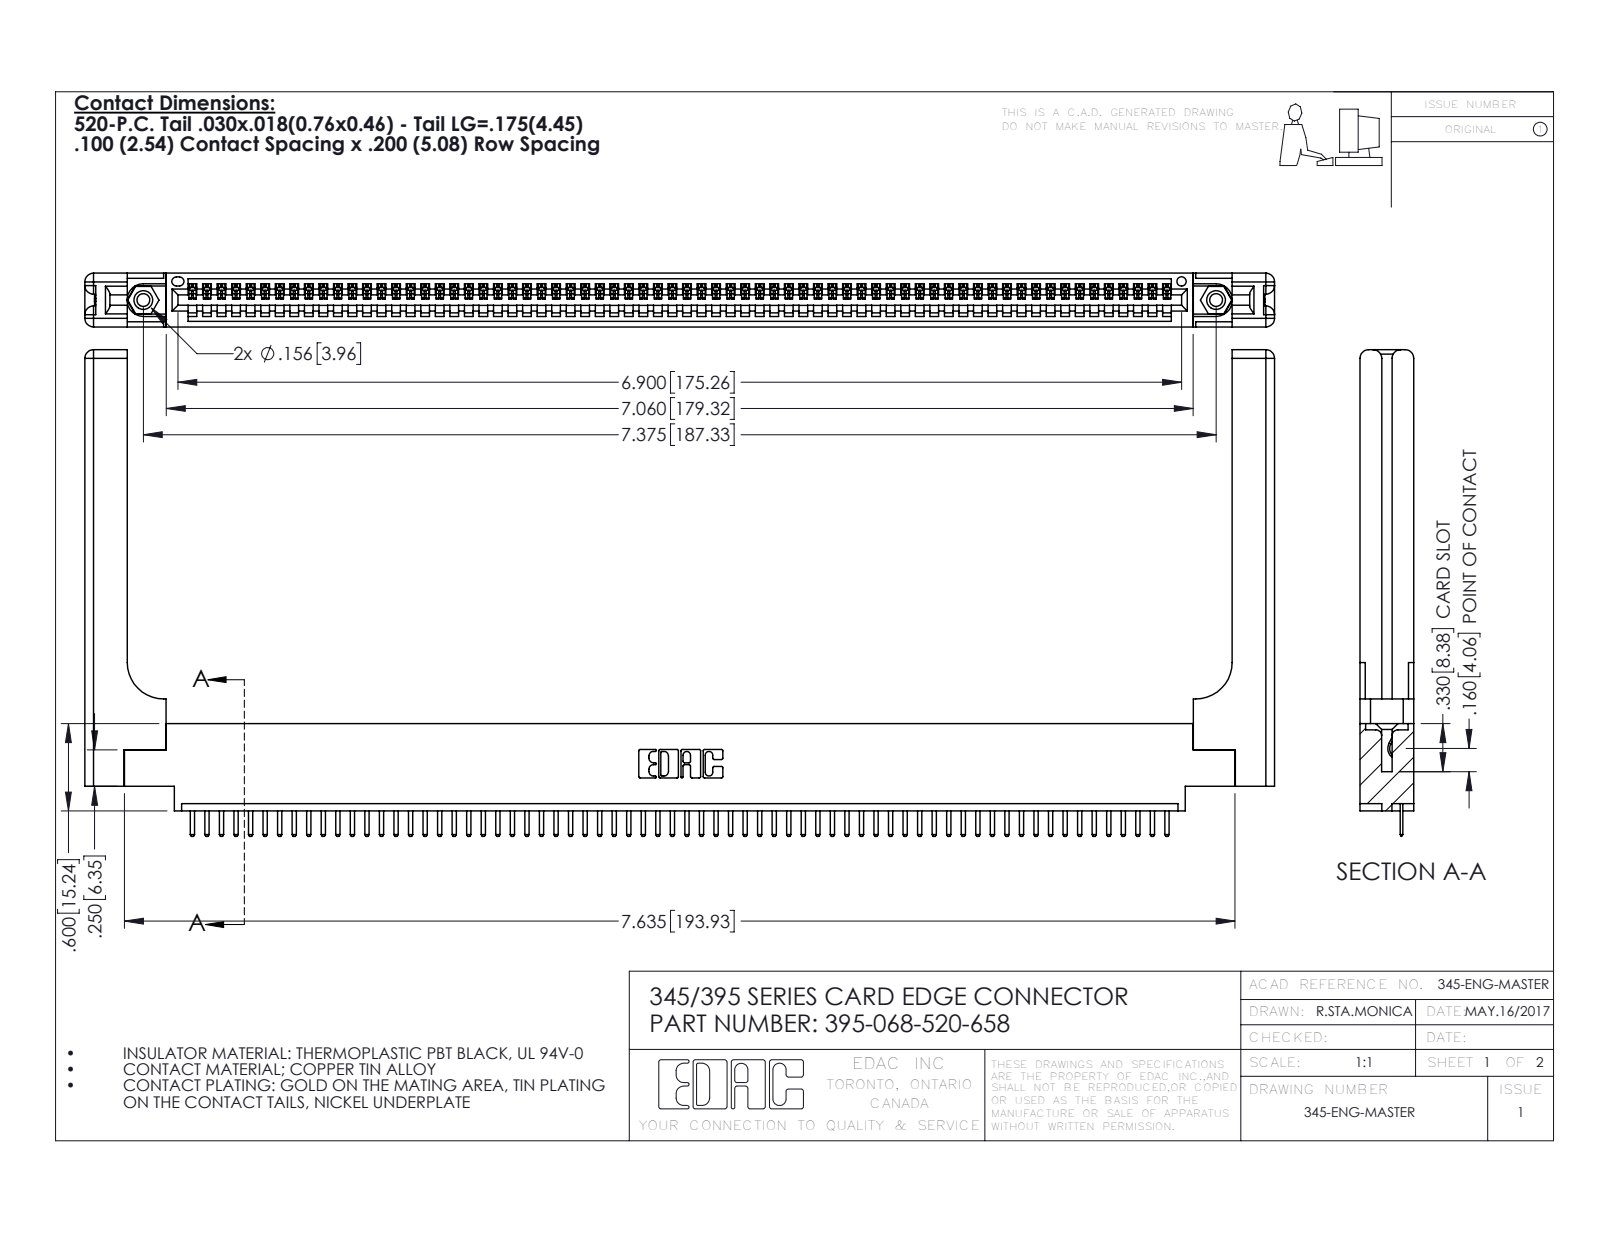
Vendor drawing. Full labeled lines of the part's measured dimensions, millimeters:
Part name (STEP PRODUCT): 345-220-058_345-220-058; 345 Part_0.170 Offset - 0.156 Dia-TH; 345-250-001_345-250-001-102; 395-068-520-658 (+1 more)
STEP written by: SolidWorks 2016 (CONFIG_CONTROL_DESIGN)
Units: millimetres
Bodies: 73 solids, 4602 faces (3088 planar, 1454 cylindrical, 60 other)
Overall size (bounding box): 207.7 × 85 × 9.4
Volume: 28 140 mm³ · Surface area: 31 240 mm²
Round holes (diameter × count): ⌀2.3 ×2, ⌀3.2 ×2, ⌀4 ×2, ⌀1.6 ×1
Round bosses / shafts (diameter × count): ⌀3.9 ×2
Partial cylindrical surfaces — rounded edges, fillets, slot ends (radius × count): R0.3 ×138, R0.2 ×136, R0.3 ×22, R1.5 ×16, R0.2 ×6, R0.8 ×6, R0.7 ×3, R0.8 ×2
Main face-to-face distances: 9.4, 1.8, 7.6, 2.5, 6.9, 0.6, 5.1, 5.7, 3.8, 3.8
Hole centre spacings: 6.9, 181.3, 187.3
